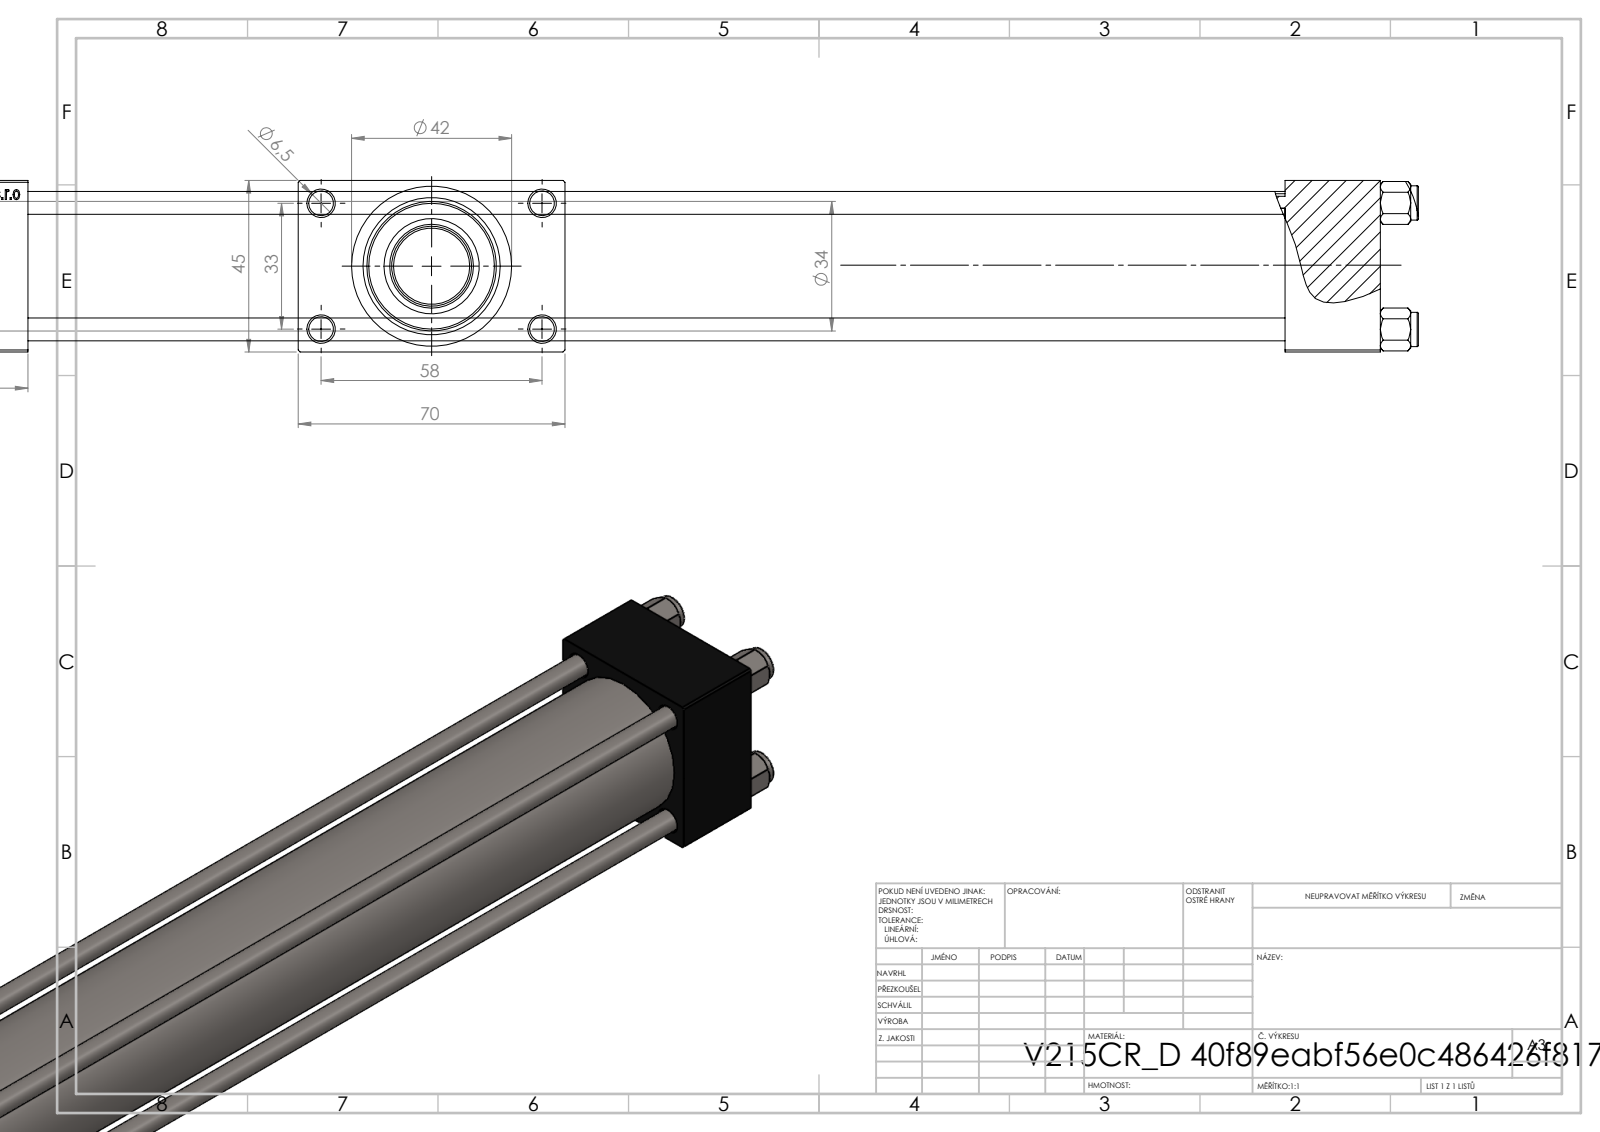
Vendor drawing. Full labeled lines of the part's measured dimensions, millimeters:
Part name (STEP PRODUCT): V215CR_ROD_END_F; V215_VC_A; V215CR_VCP_D; V215CR_D_Body (+2 more)
STEP written by: SolidWorks 2019 (CONFIG_CONTROL_DESIGN)
Units: millimetres
Bodies: 12 solids, 1115 faces (499 planar, 92 cylindrical, 524 other)
Overall size (bounding box): 466 × 70 × 45
Volume: 480 043 mm³ · Surface area: 184 082 mm²
Round holes (diameter × count): ⌀6 ×4, ⌀6.5 ×4, ⌀7 ×2, ⌀13.16 ×2, ⌀20 ×2, ⌀10.5 ×1, ⌀22 ×1, ⌀24 ×1, ⌀25 ×1, ⌀32 ×1, ⌀33 ×1
Round bosses / shafts (diameter × count): ⌀9 ×4, ⌀42 ×1, ⌀38 ×1, ⌀34 ×1, ⌀21 ×1, ⌀13 ×1
Main face-to-face distances: 45, 25, 12.5, 330, 355, 57.5, 368, 38, 393, 70
Hole centre spacings: 12.4, 23.48, 33.2, 33.37, 35.35, 45.6, 56.35, 33
